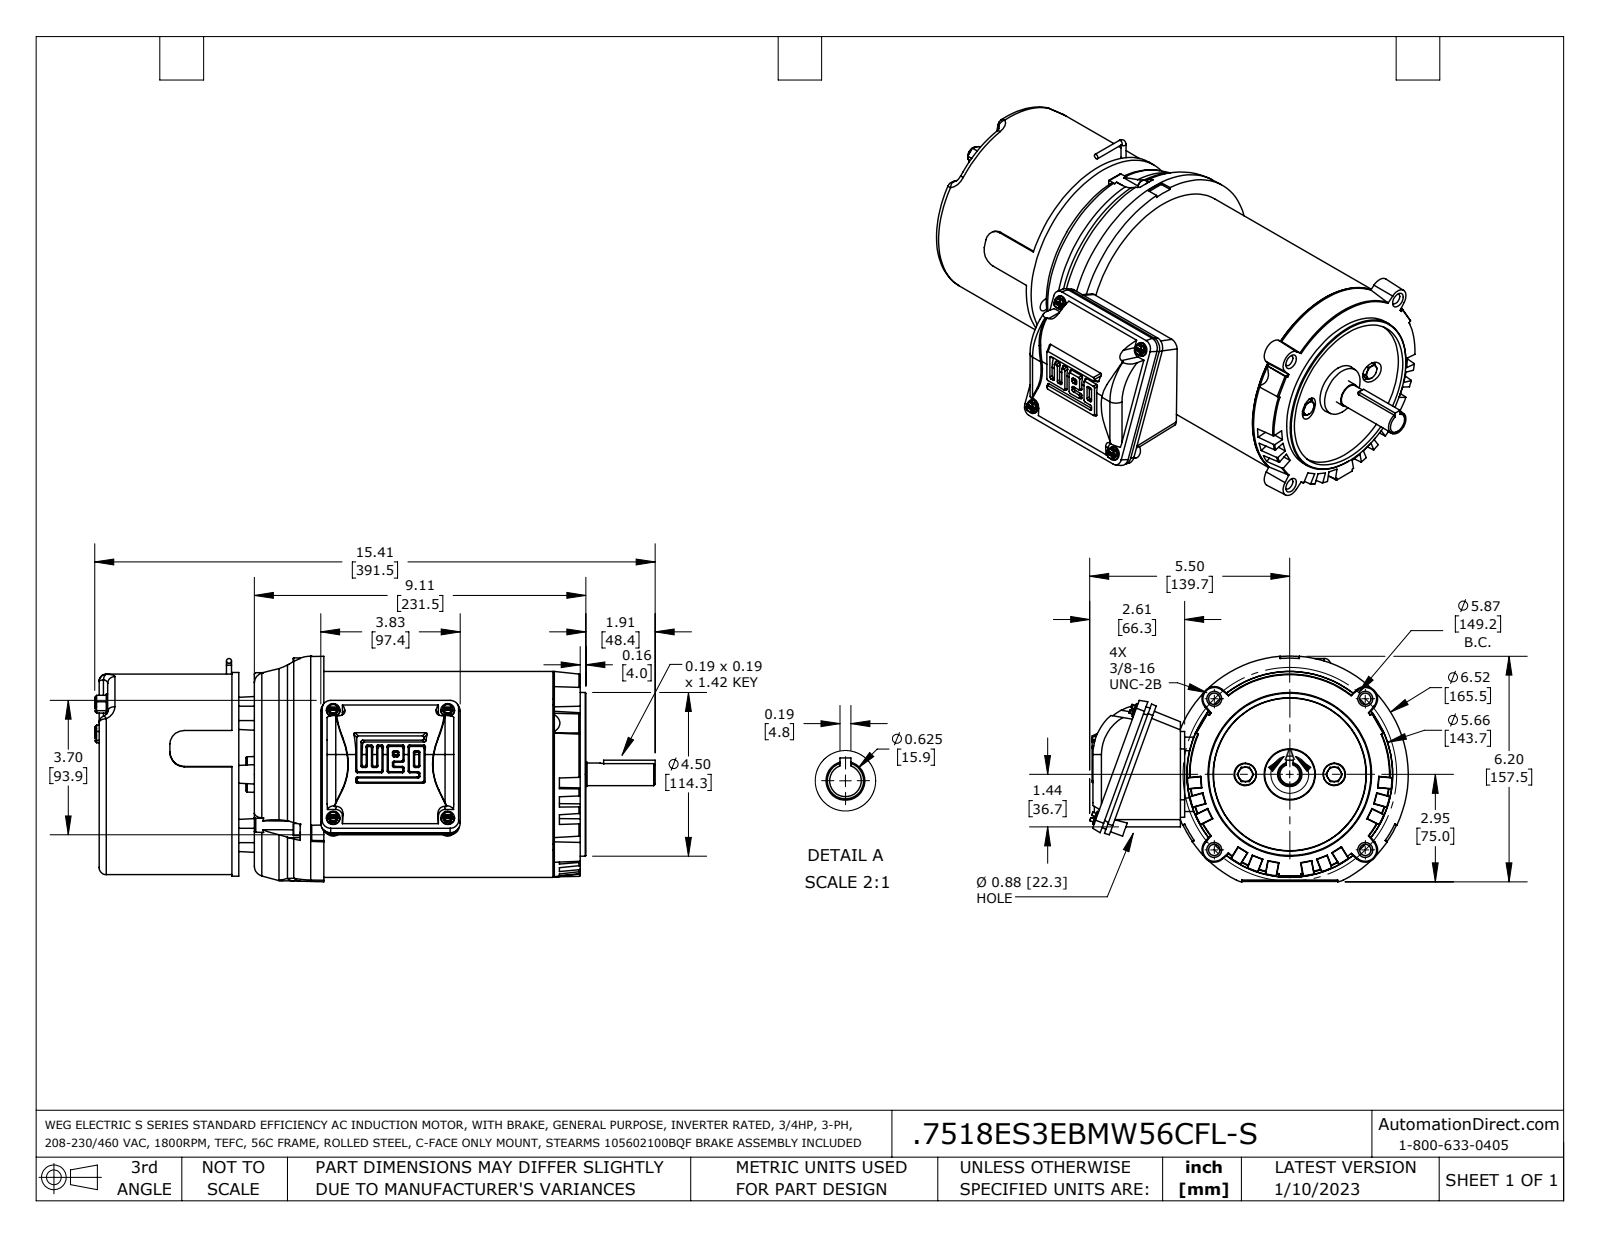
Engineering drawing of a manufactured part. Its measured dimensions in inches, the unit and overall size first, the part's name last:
Units: inches
Overall size (bounding box): 15.411 × 8.76 × 6.202
Round holes (diameter × count): ⌀0.236 ×4, ⌀0.313 ×4, ⌀0.25 ×2, ⌀0.28 ×2, ⌀0.37 ×2, ⌀0.5 ×1, ⌀3 ×1
Round bosses / shafts (diameter × count): ⌀0.374 ×4, ⌀0.187 ×4, ⌀0.335 ×3, ⌀0.197 ×3, ⌀0.551 ×2, ⌀0.437 ×2, ⌀0.138 ×2, ⌀5.659 ×1
Partial cylindrical surfaces — rounded edges, fillets, slot ends (radius × count): R0.047 ×38, R0.197 ×10, R0.205 ×8, R0.02 ×4, R0.276 ×4, R0.374 ×4, R0.48 ×4, R0.039 ×3
Main face-to-face distances: 6.299, 0.571, 6.87, 1.772, 7.913, 1.043, 1.614, 0.728, 2.343, 8.642
Hole centre spacings: 2.087, 2.937, 4.154, 4.463, 3.15, 0.718, 0.975, 1.483
Volume: 321.3 in³ · Surface area: 652.4 in²
Bodies: 15 solids, 1176 faces (471 planar, 231 cylindrical, 474 other)
Part name (STEP PRODUCT): W56C_3PH_TEFC_BM_15398_FL coord fxt
STEP written by: SolidWorks 2021 (AUTOMOTIVE_DESIGN)
